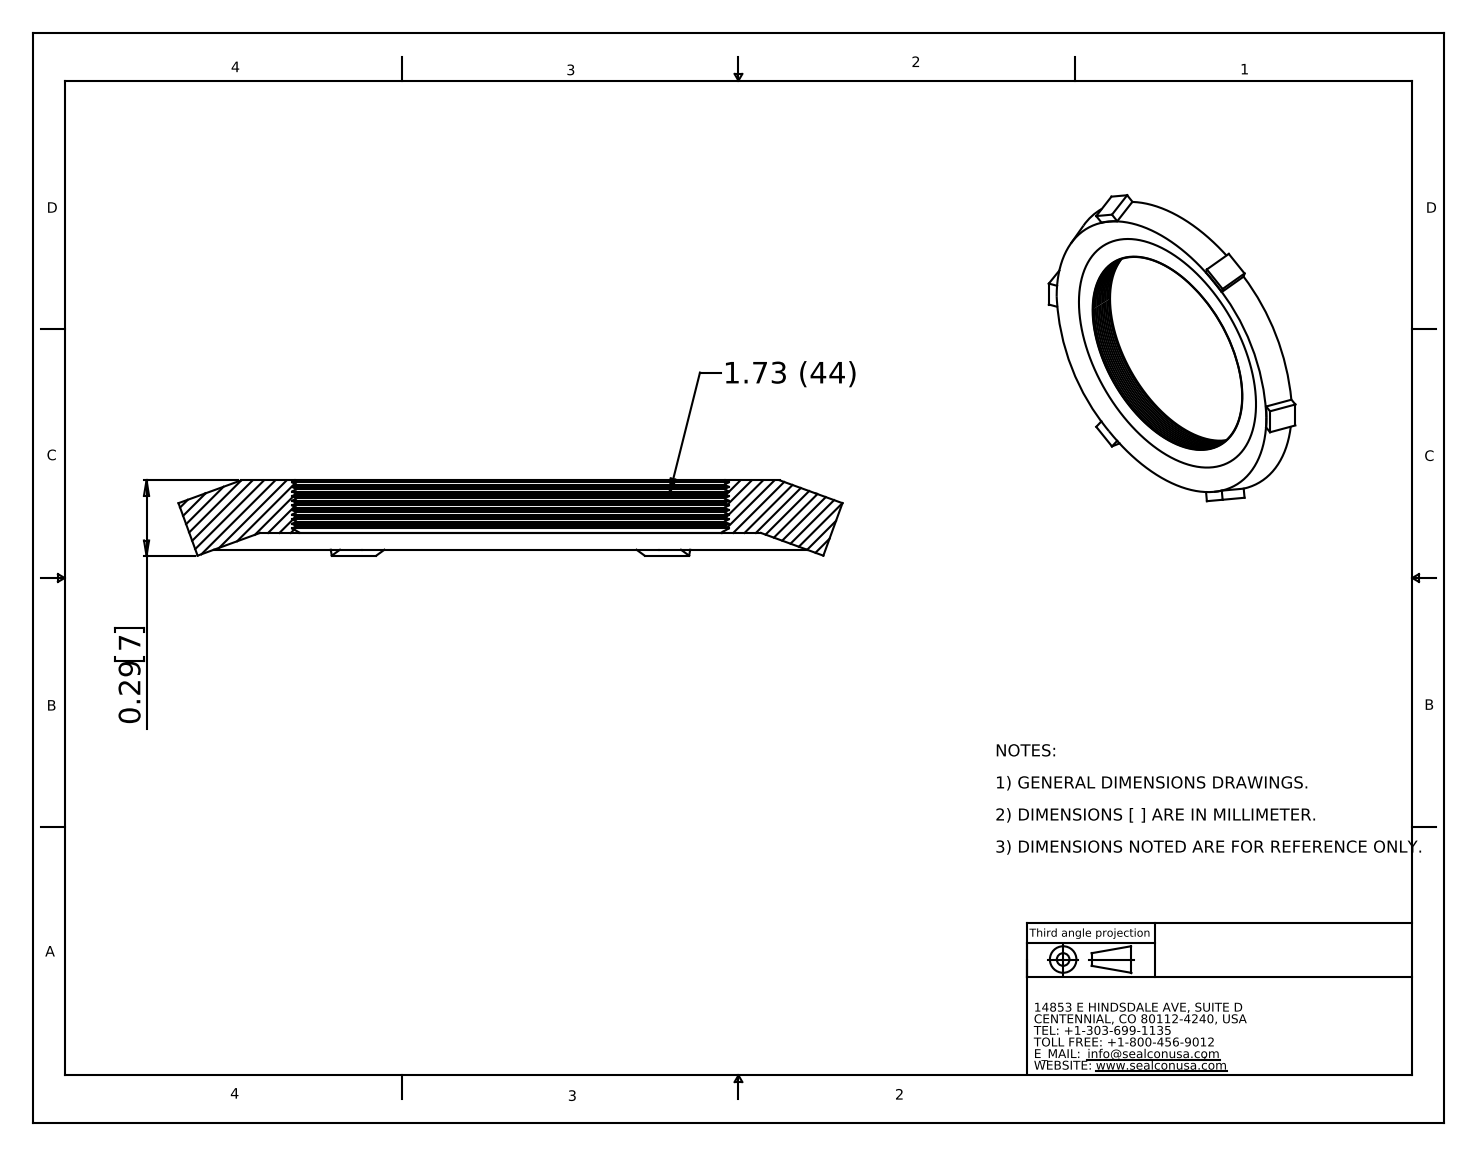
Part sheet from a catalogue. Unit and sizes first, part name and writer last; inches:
Units: inches
Overall size (bounding box): 2.587 × 2.46 × 0.293
Main face-to-face distances: 0.204, 0.2, 0.218, 0.11, 0.11
Volume: 0.511 in³ · Surface area: 8.919 in²
Bodies: 1 solid, 100 faces (44 planar, 0 cylindrical, 56 other)
Part name (STEP PRODUCT): NN-10-ST
STEP written by: SolidWorks 2008 (CONFIG_CONTROL_DESIGN)
